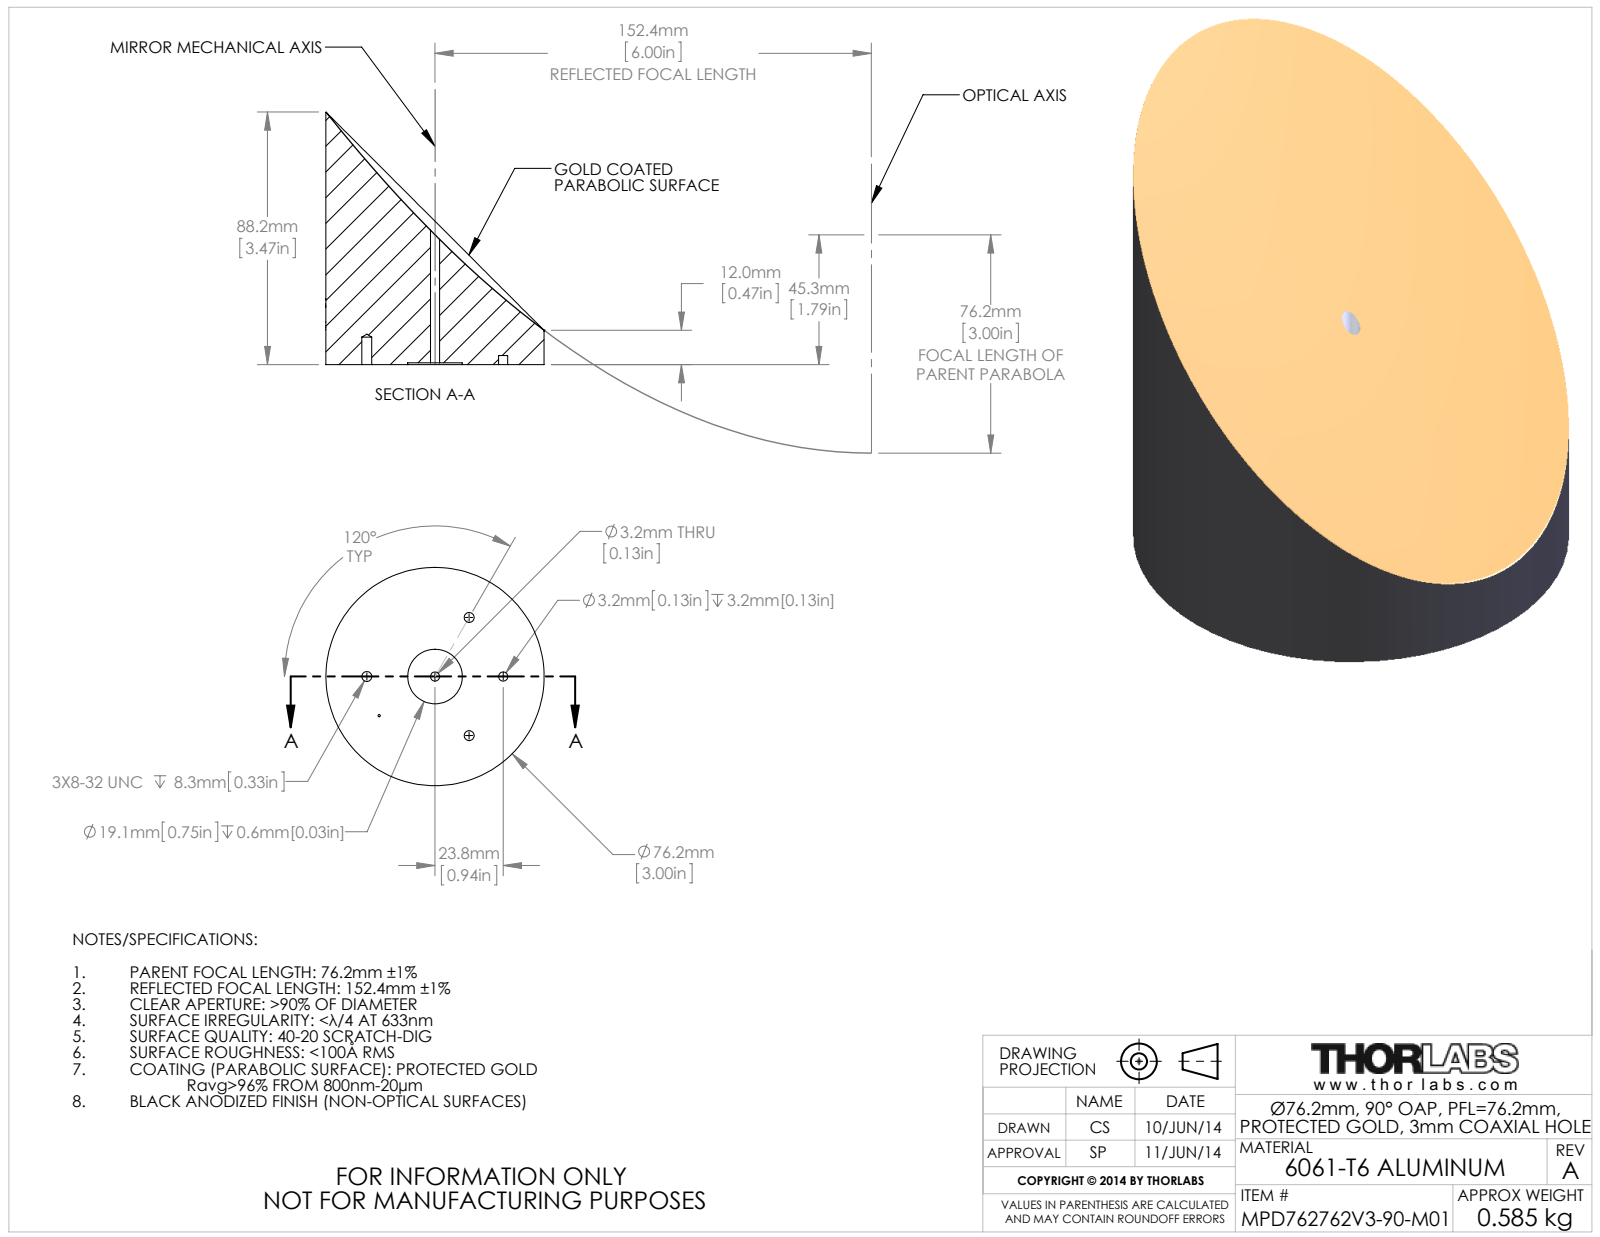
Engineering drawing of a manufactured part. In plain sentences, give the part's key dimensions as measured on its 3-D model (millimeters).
The part is named "TTN028515-E0W". Its 3-D file was written by "SolidWorks 2014 (CONFIG_CONTROL_DESIGN)". It is 1 solid with 67 faces: 3 planar, 52 cylindrical and 12 other. Overall it measures 88.1 by 76.2 by 76.2 millimeters. Its volume is 216 600 cubic millimeters and its surface area 23 830 square millimeters. Round holes: 3 of diameter 3.5, 2 of diameter 3.2, 1 of diameter 19.1. Round bosses or shafts: 1 of diameter 76.2. The main face-to-face distances are 0.6, 3.2, 2.5. The hole center spacings are 23.8, 23.8, 41.2, 41.2, 47.6.
